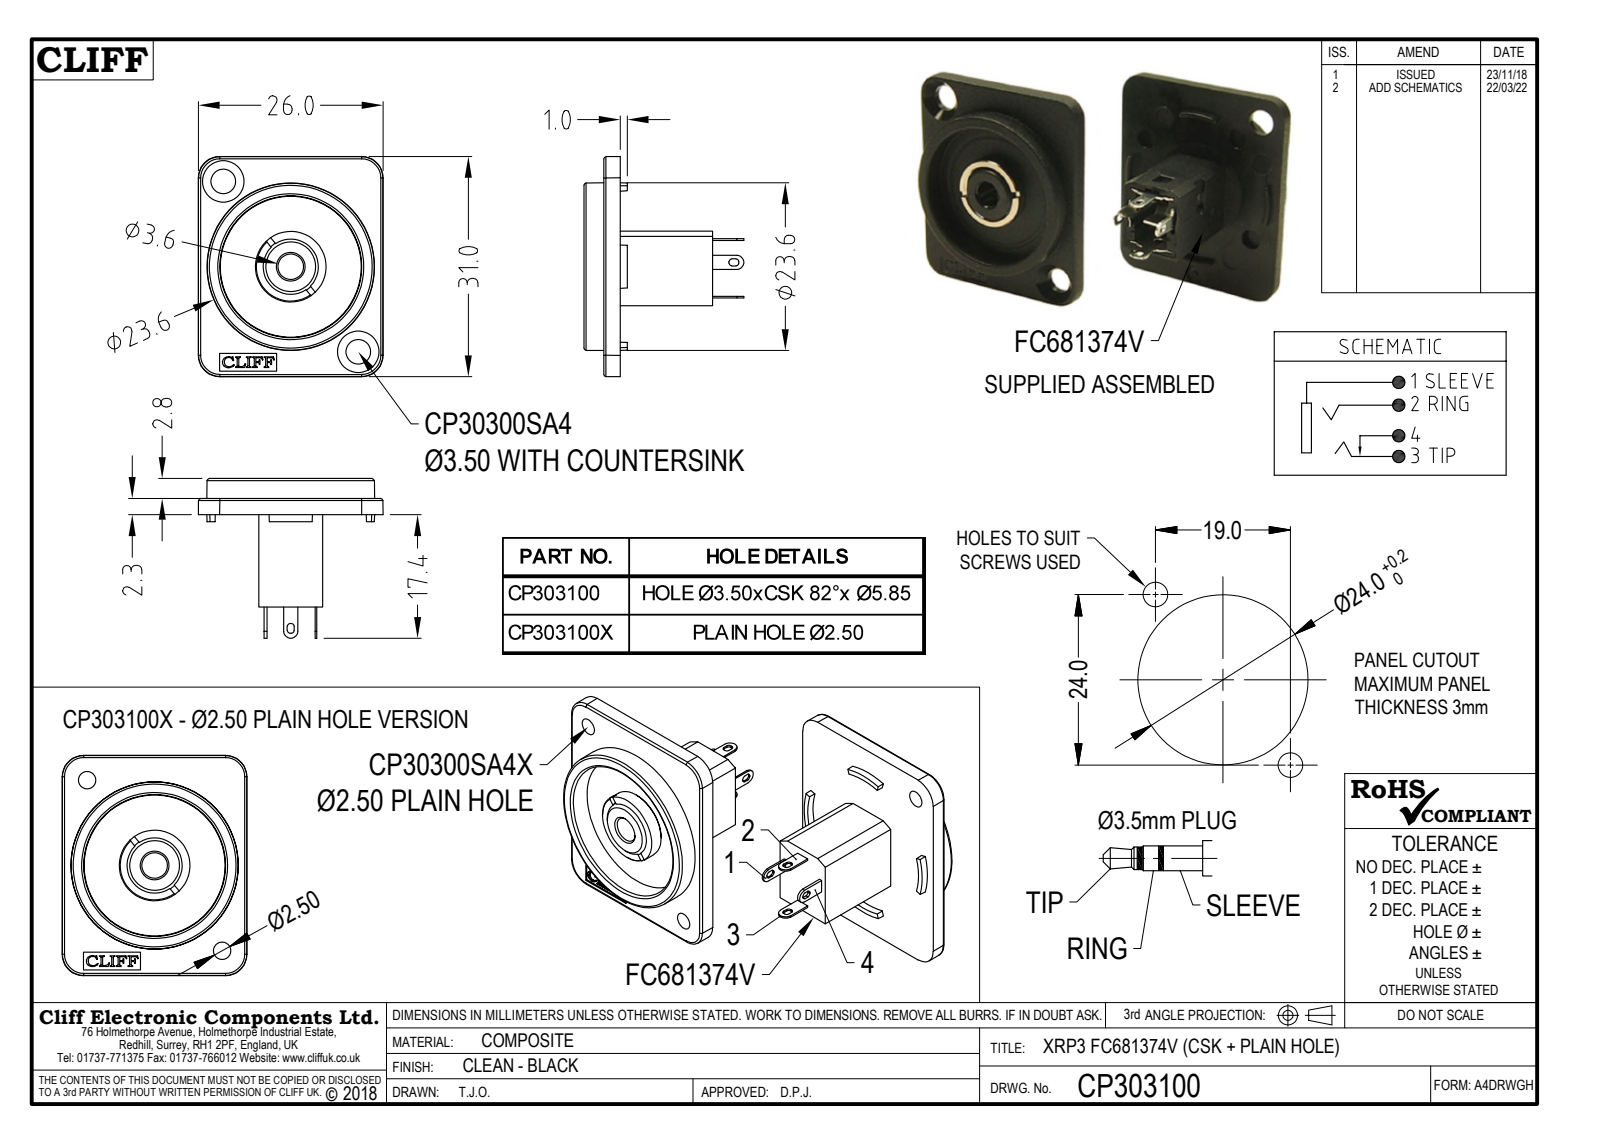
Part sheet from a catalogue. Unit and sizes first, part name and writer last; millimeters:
Units: millimetres
Overall size (bounding box): 31 × 26 × 22.5
Round holes (diameter × count): ⌀3.5 ×2, ⌀3.6 ×1, ⌀8.1 ×1
Round bosses / shafts (diameter × count): ⌀10 ×1, ⌀8 ×1
Partial cylindrical surfaces — rounded edges, fillets, slot ends (radius × count): R0.4 ×8, R0.3 ×4, R3 ×4, R1 ×2
Main face-to-face distances: 2.1, 2.3, 9, 5.1, 15.3, 15.1, 13, 10.5, 3, 2.8
Hole centre spacings: 15.31, 30.61
Volume: 3 282 mm³ · Surface area: 3 238 mm²
Bodies: 1 solid, 269 faces (155 planar, 39 cylindrical, 75 other)
Part name (STEP PRODUCT): CP303100
STEP written by: Autodesk Inventor 2026 (AUTOMOTIVE_DESIGN)
